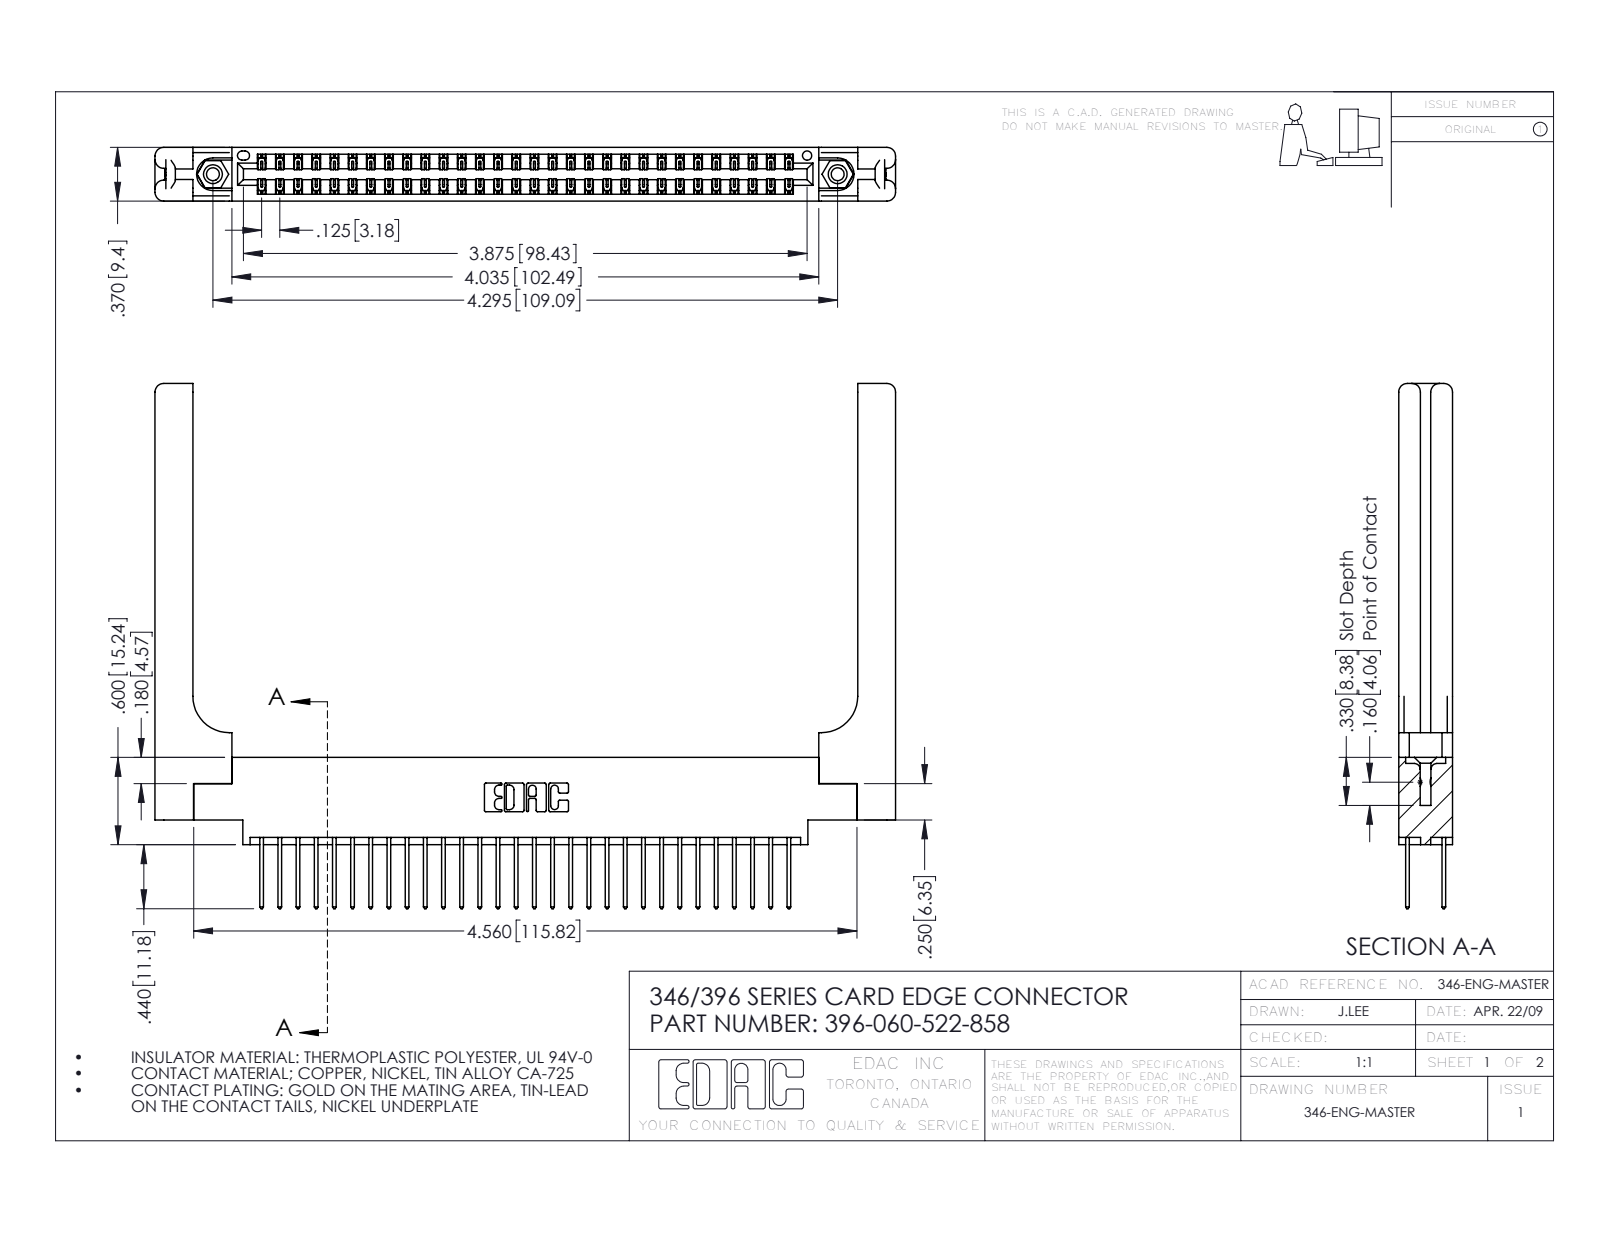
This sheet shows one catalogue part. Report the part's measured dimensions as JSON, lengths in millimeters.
{"part_name": "346-220-058_345-220-058; 345-250-001_345-250-001-102; 396-060-522-858; 346 Part_0.170 Offset - 0.156 Dia-TH (+1 more)", "step_written_by": "SolidWorks 2016 (CONFIG_CONTROL_DESIGN)", "units": "millimeters", "bodies": {"solids": 65, "faces": 3502, "planar": 2328, "cylindrical": 1114, "other": 60}, "overall_size": [129.3, 91.7, 9.4], "volume_mm3": 20010, "surface_area_mm2": 22880, "round_holes": [[2.3, 2], [3.2, 2], [4, 2], [1.6, 1]], "round_bosses_or_shafts": [[3.9, 2]], "partial_cylinders_radius": [[0.2, 90], [0.3, 60], [0.3, 22], [1.5, 16], [0.2, 6], [0.8, 6], [0.7, 3], [0.4, 2]], "face_to_face_distances": [9.4, 1.2, 8.2, 1.8, 6.4, 3.8, 3.8, 0.6, 7.6, 7], "hole_center_spacings": [6.2, 103.8, 109.1]}
